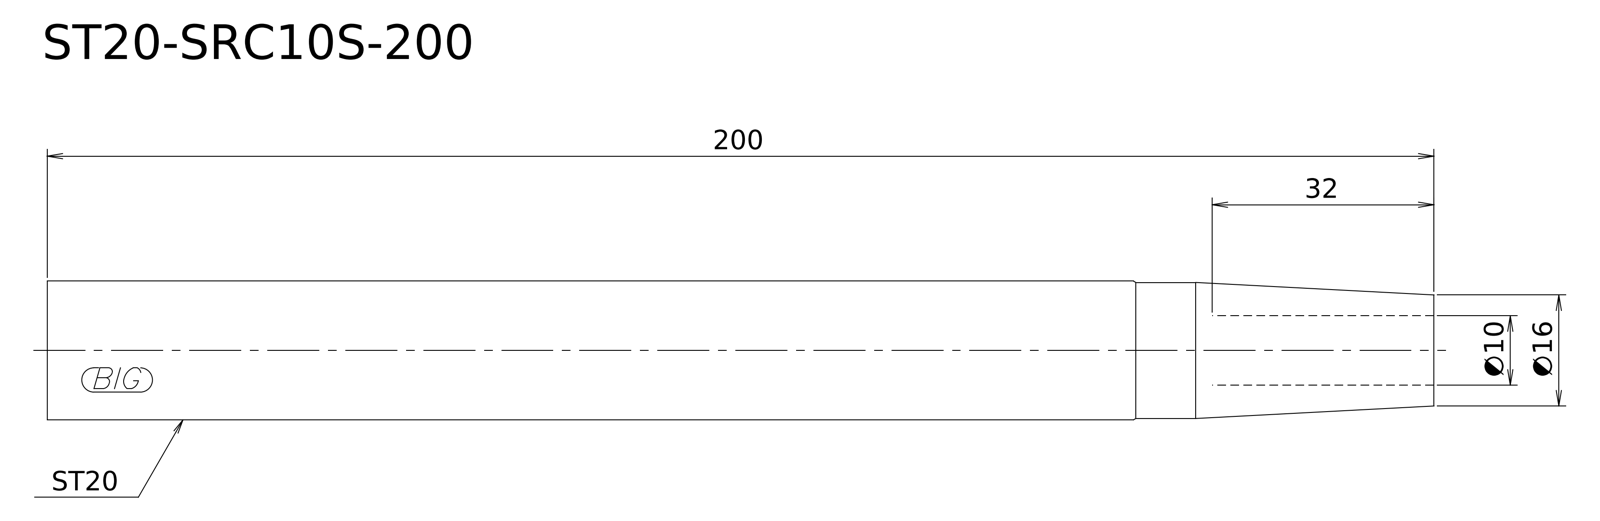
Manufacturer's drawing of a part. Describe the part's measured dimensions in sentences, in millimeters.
Its 3-D file was written by "Kubotek KeyCreator V8.5.1 (14335) (CONFIG_CONTROL_DESIGN)". It is 1 solid with 6 faces: 2 planar, 2 cylindrical and 2 other. Overall it measures 200 by 20 by 20 millimeters. Its volume is 60 508 cubic millimeters and its surface area 12 839 square millimeters. Round bosses or shafts: 1 of diameter 20, 1 of diameter 19.6. The main face-to-face distances are 200.
